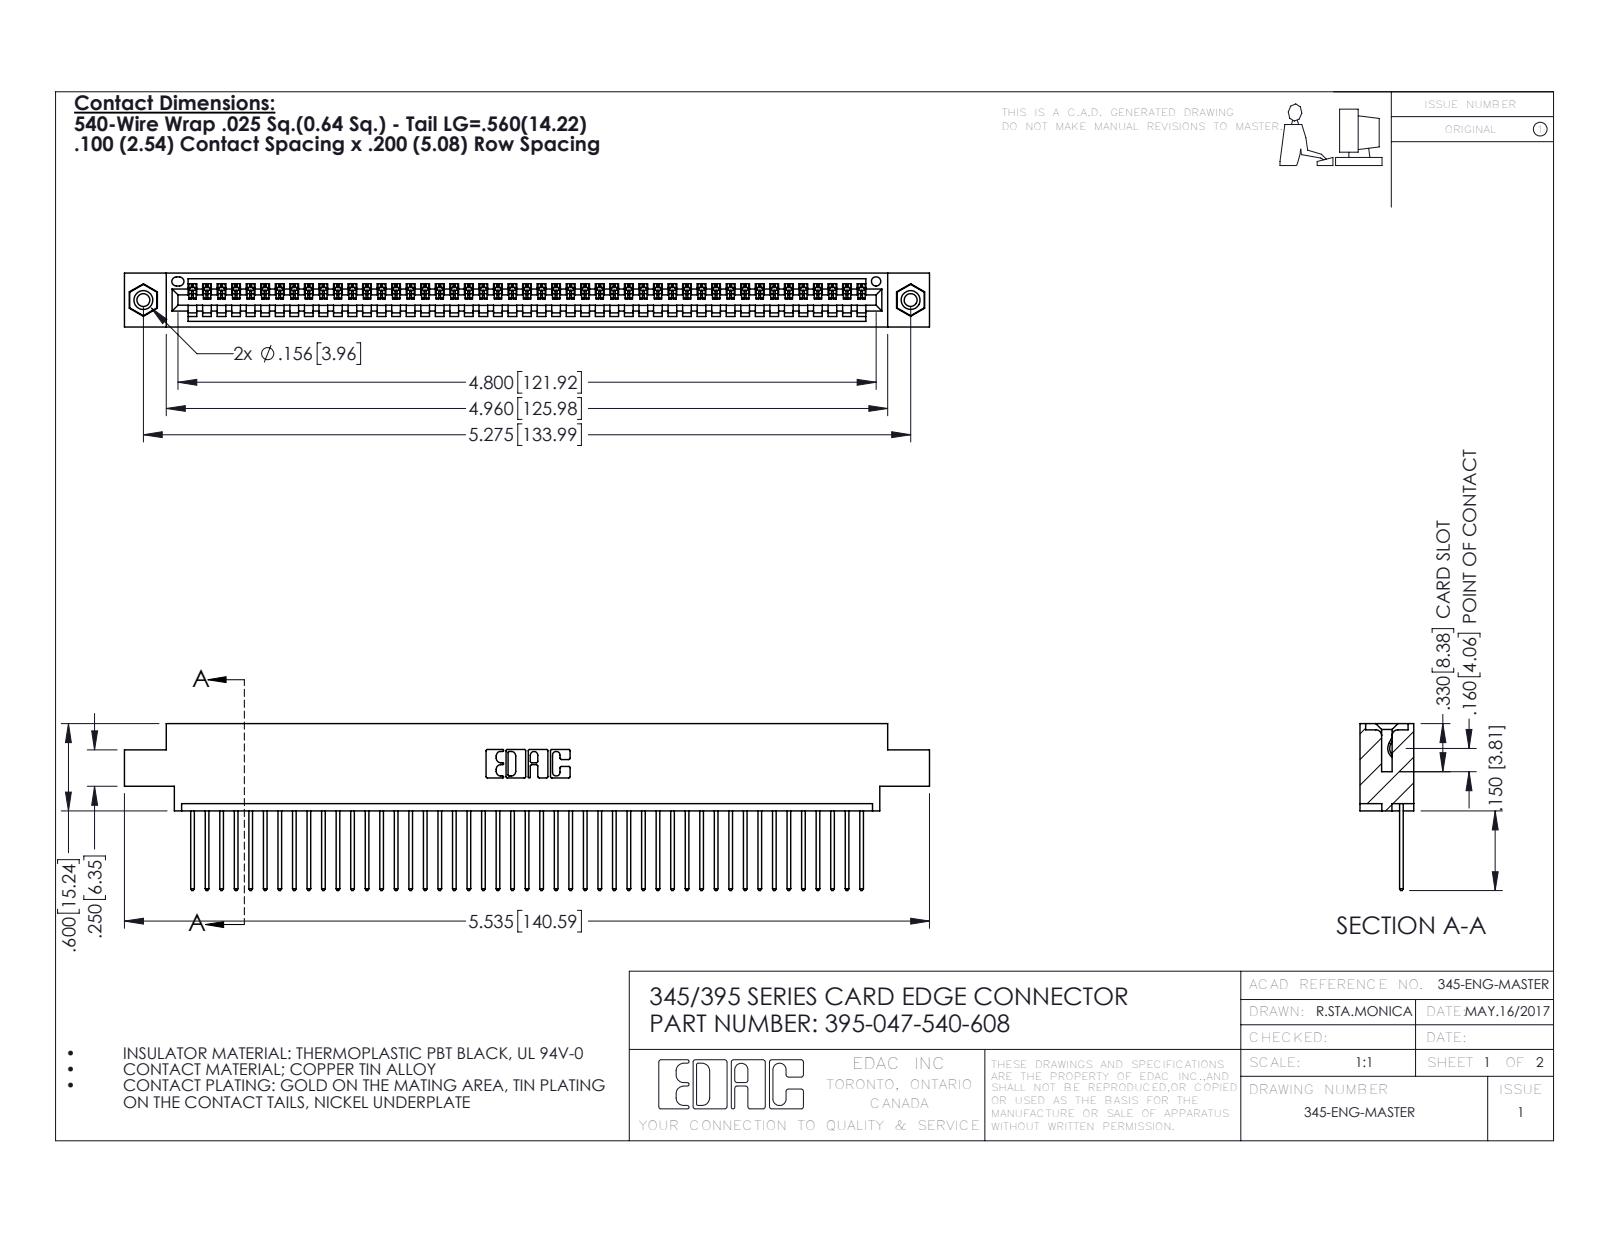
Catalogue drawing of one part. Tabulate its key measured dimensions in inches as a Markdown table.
| quantity | value |
| --- | --- |
| part name | 395-047-540-608; 345-250-001_345-250-003-102; 345-292-001_345-293-140; 345 Part_0.170 Offset - 0.156 Dia-TI |
| STEP written by | SolidWorks 2016 (CONFIG_CONTROL_DESIGN) |
| units | inches |
| bodies | 50 solids, 2916 faces (1996 planar, 904 cylindrical, 16 other) |
| overall size | 5.535 × 1.147 × 0.37 |
| volume | 0.814 in³ |
| surface area | 28.51 in² |
| round holes (diameter × count) | 0.089 × 2, 0.125 × 2, 0.156 × 2, 0.064 × 1 |
| round bosses / shafts (diameter × count) | 0.155 × 2 |
| partial cylindrical surfaces (radius × count) | 0.006 × 94, 0.01 × 94, 0.01 × 22, 0.007 × 6, 0.031 × 6, 0.026 × 3, 0.031 × 2, 0.04 × 2 |
| main face-to-face distances | 0.072, 0.298, 0.37, 0.098, 0.272, 0.025, 0.2, 0.225, 0.175, 0.149 |
| hole center spacings | 0.27, 5.039, 5.275 |
